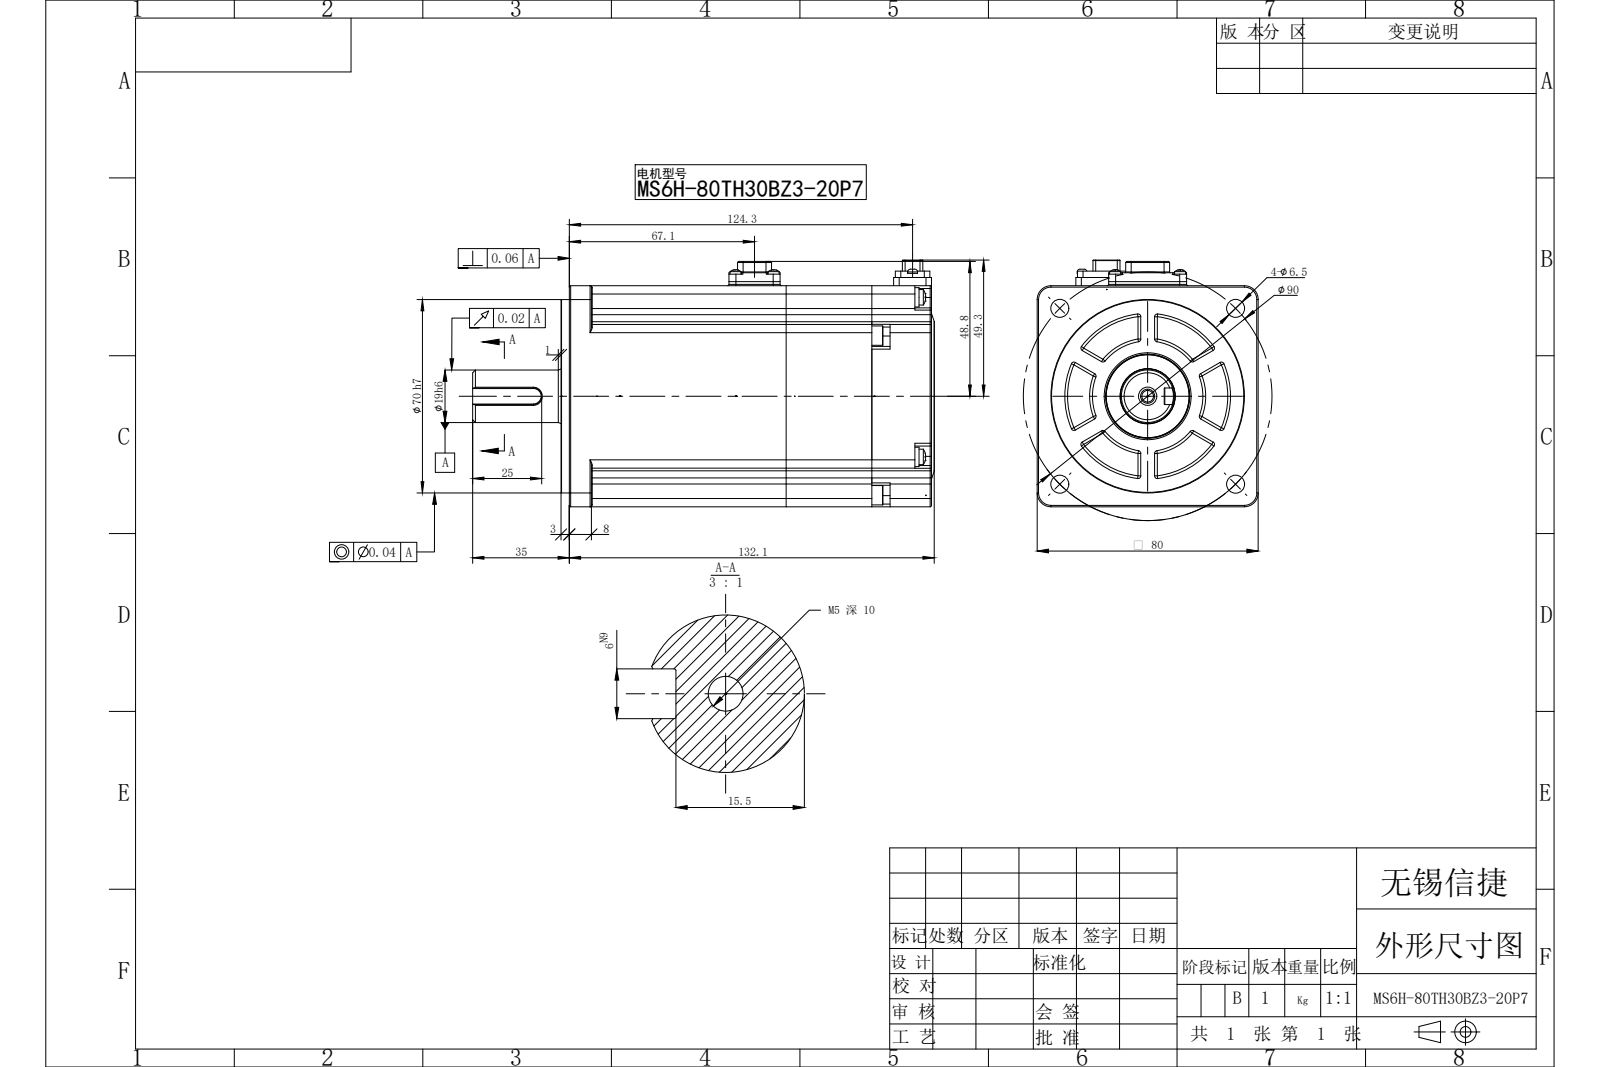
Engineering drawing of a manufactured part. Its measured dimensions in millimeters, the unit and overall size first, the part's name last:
Units: millimetres
Overall size (bounding box): 167.1 × 89.3 × 80
Round holes (diameter × count): ⌀2.1 ×4, ⌀6.5 ×4, ⌀1.6 ×2, ⌀4.2 ×1, ⌀20 ×1
Round bosses / shafts (diameter × count): ⌀7 ×8, ⌀5.6 ×4, ⌀4 ×4, ⌀3.5 ×2, ⌀70 ×1, ⌀30 ×1, ⌀19.8 ×1, ⌀19 ×1
Partial cylindrical surfaces — rounded edges, fillets, slot ends (radius × count): R1 ×50, R0.5 ×39, R3 ×17, R0.2 ×15, R0.3 ×14, R2 ×12, R3.75 ×8, R0.6 ×4
Main face-to-face distances: 80, 14, 66, 131.1, 52, 1, 132.1, 3, 135.1, 134.1
Hole centre spacings: 45, 63.64, 8, 16.6, 18.43, 90, 23.5, 53.45
Bodies: 0 solids, 881 faces (377 planar, 318 cylindrical, 186 other)
Part name (STEP PRODUCT): MS6H-80TH30BZ3-20P7
STEP written by: SolidWorks 2022 (CONFIG_CONTROL_DESIGN)
